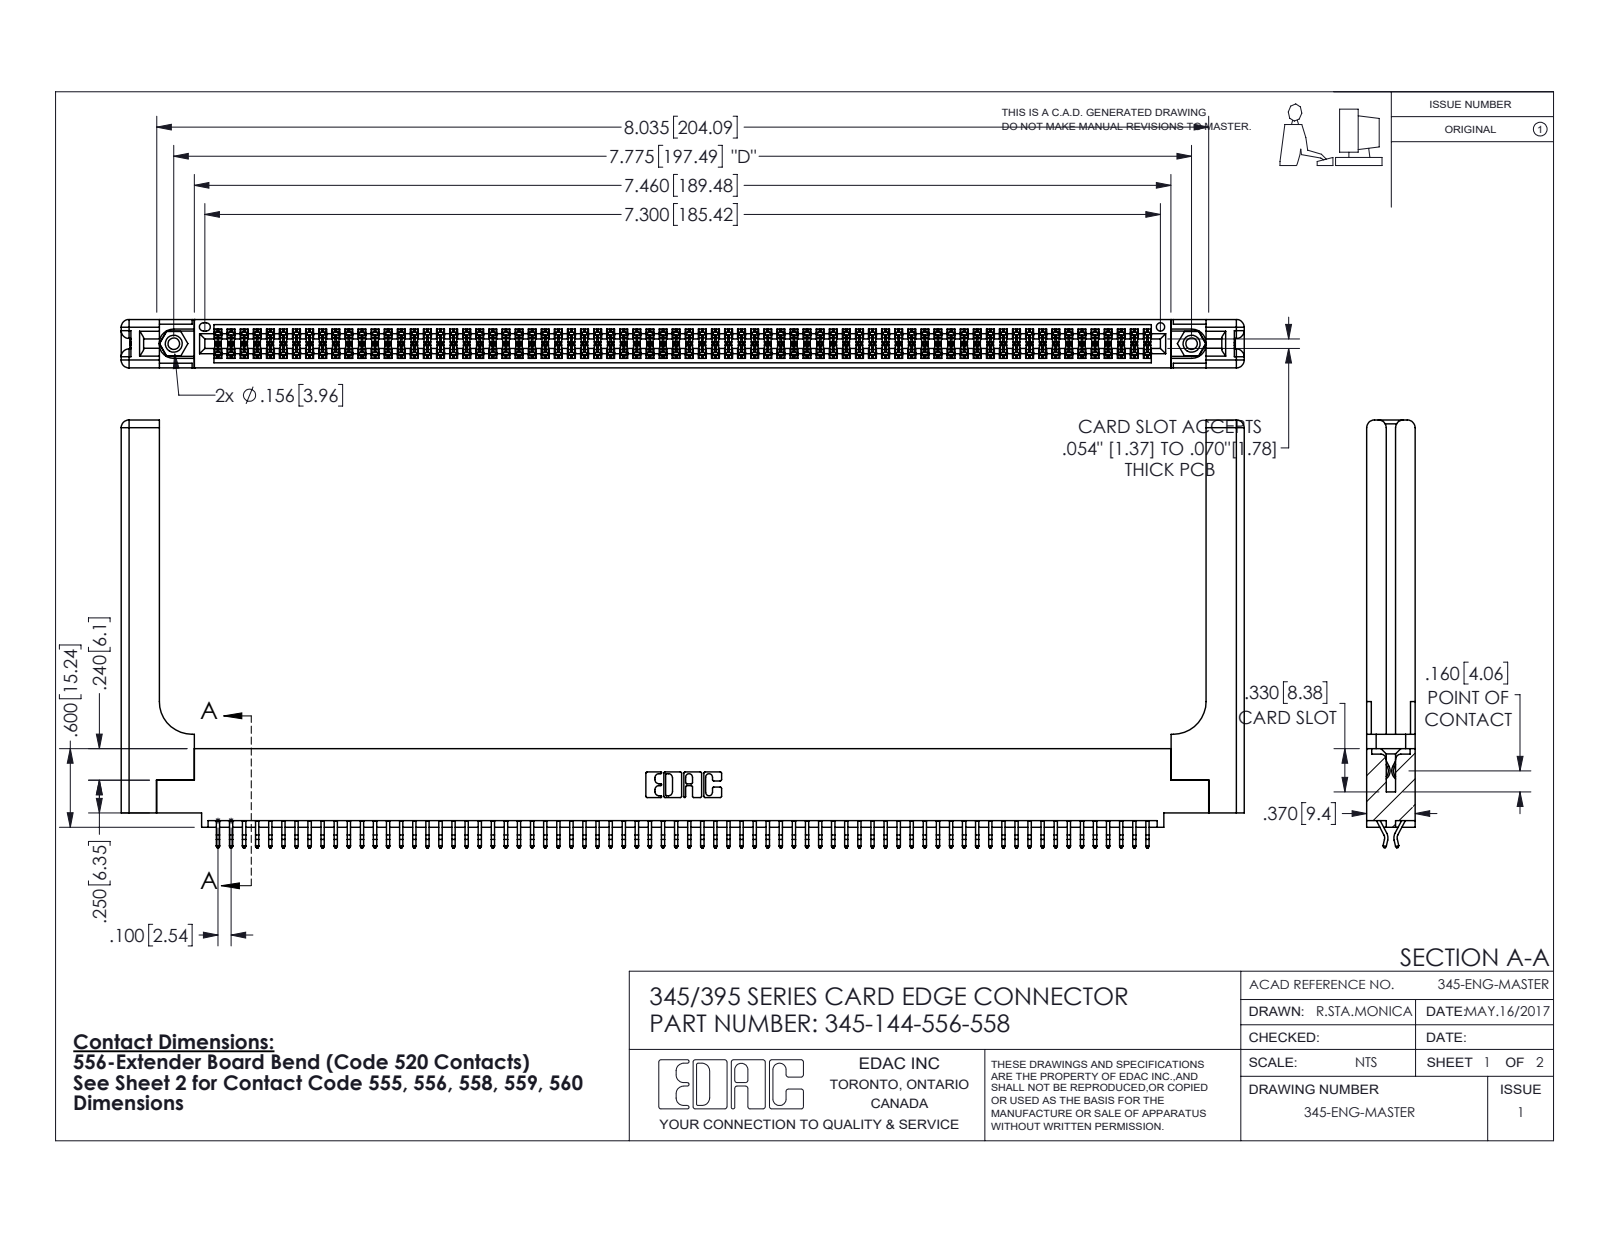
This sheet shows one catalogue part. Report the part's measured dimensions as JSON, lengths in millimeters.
{"part_name": "345-220-058_345-220-058; 345 Part_0.110 Offset - 0.156 Dia-TH; 345-144-556-558; 345-250-001_345-250-001-102 (+1 more)", "step_written_by": "SolidWorks 2016 (CONFIG_CONTROL_DESIGN)", "units": "millimeters", "bodies": {"solids": 149, "faces": 8450, "planar": 5560, "cylindrical": 2830, "other": 60}, "overall_size": [217.9, 83, 9.4], "volume_mm3": 29840, "surface_area_mm2": 37190, "round_holes": [[2.3, 2], [3.2, 2], [4, 2], [1.6, 1]], "round_bosses_or_shafts": [[3.9, 2]], "partial_cylinders_radius": [[0.2, 216], [0.3, 22], [1.5, 16], [0.2, 6], [0.8, 6], [0.7, 3], [0.3, 2], [0.4, 2]], "face_to_face_distances": [1.8, 7.6, 9.4, 0.6, 2.5, 6.9, 5.1, 5.7, 4.4, 3.8], "hole_center_spacings": [6.9, 191.5, 197.5]}
